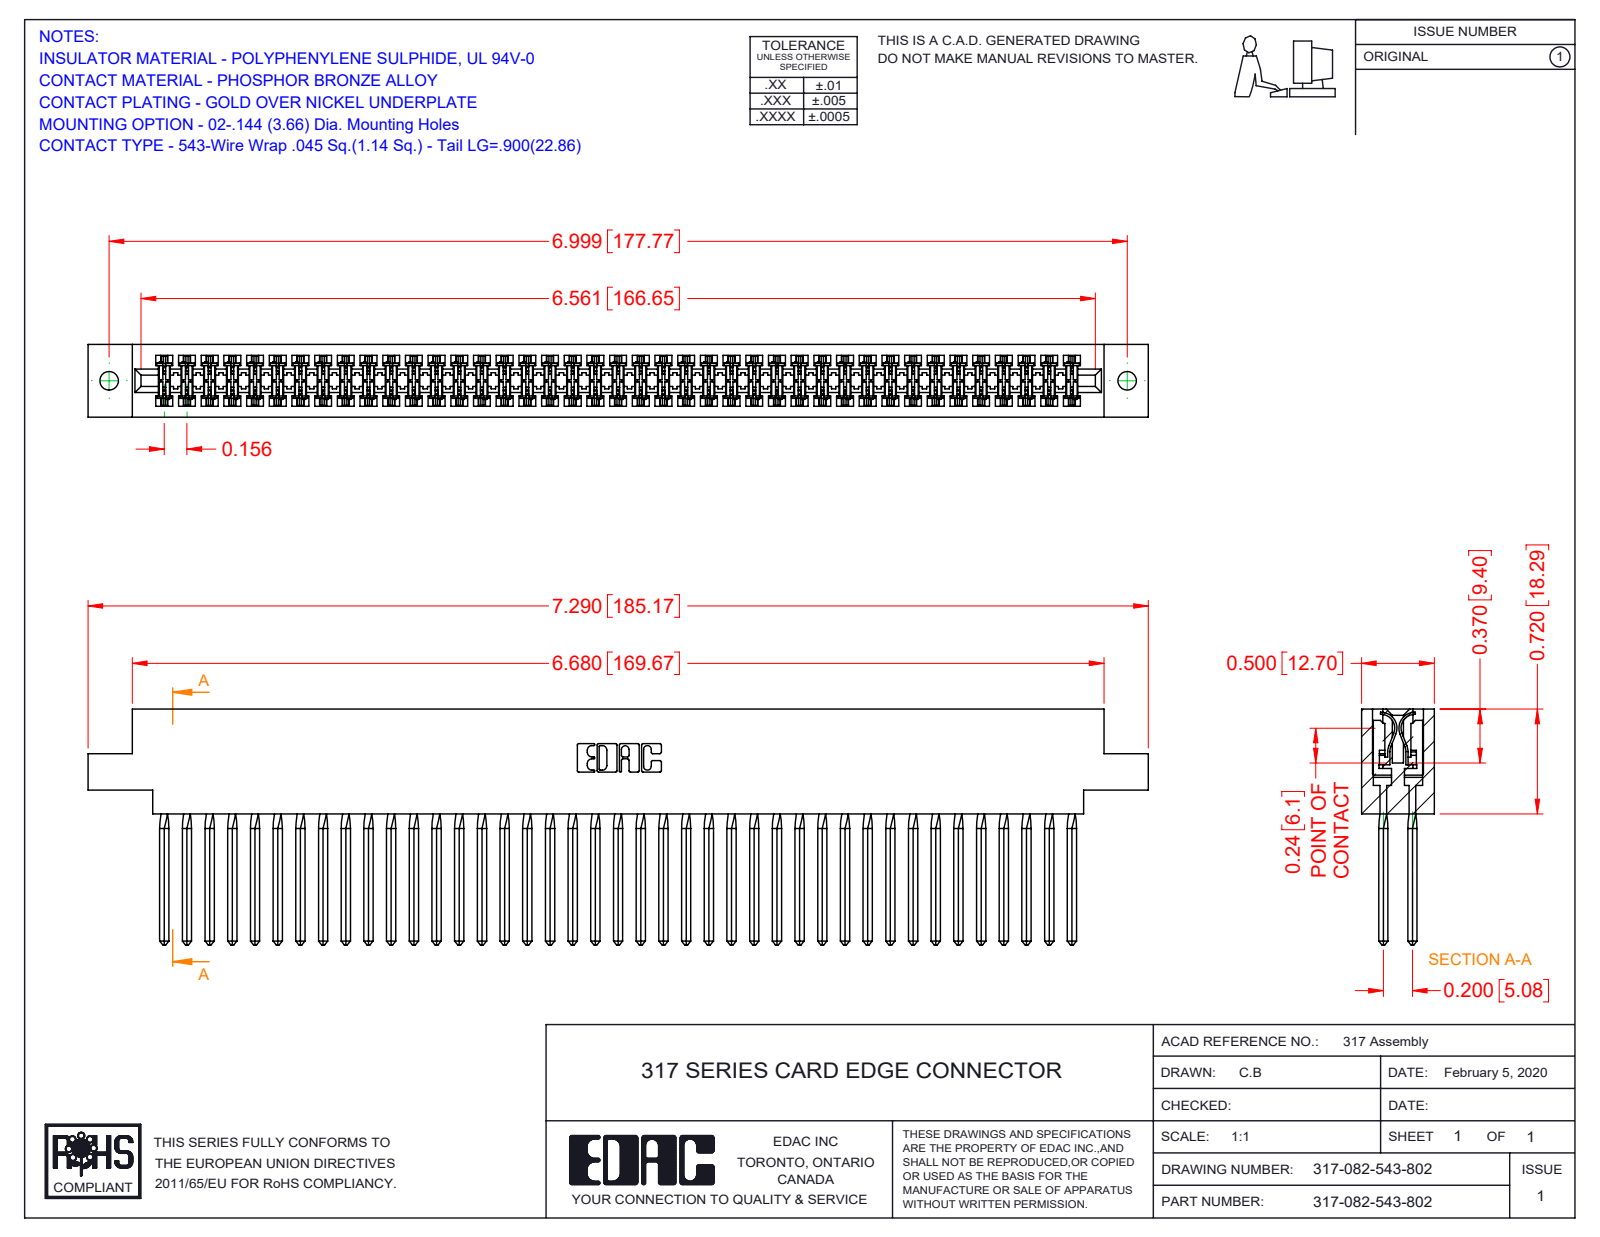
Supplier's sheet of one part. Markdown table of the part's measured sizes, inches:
| quantity | value |
| --- | --- |
| part name | 317-082-543-802; 317 Part_.144 Dia; 317-290-001_543 |
| STEP written by | SolidWorks 2016 (CONFIG_CONTROL_DESIGN) |
| units | inches |
| bodies | 83 solids, 7400 faces (6044 planar, 1028 cylindrical, 328 other) |
| overall size | 7.29 × 1.62 × 0.5 |
| volume | 1.917 in³ |
| surface area | 73.4 in² |
| round holes (diameter × count) | 0.128 × 2 |
| partial cylindrical surfaces (radius × count) | 0.015 × 164, 0.01 × 22, 0.007 × 6, 0.031 × 6, 0.026 × 3, 0.095 × 2, 0.1 × 2, 0.11 × 2 |
| main face-to-face distances | 0.5, 0.075, 0.425, 0.35, 0.195, 0.11, 0.094, 0.2, 0.115, 0.131 |
| hole center spacings | 6.999 |
